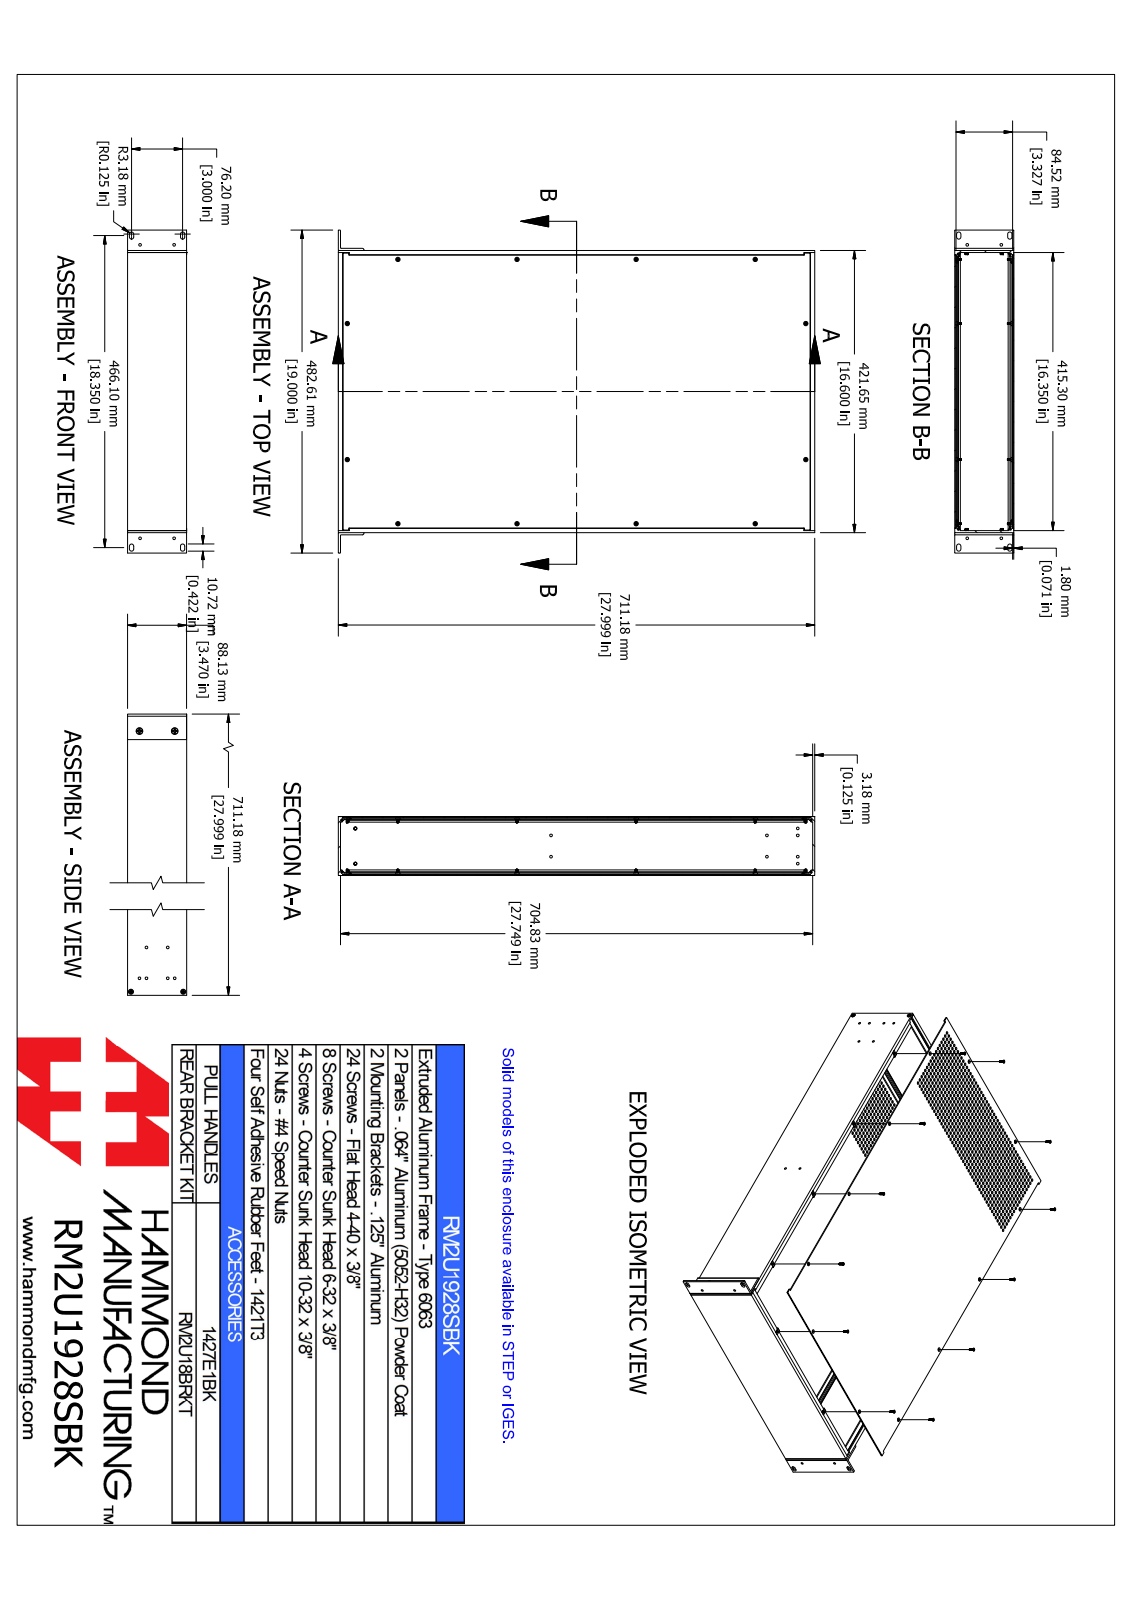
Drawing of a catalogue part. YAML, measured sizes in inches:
part_name: "RM2U1928SBK"
step_written_by: "SolidWorks 2021 (AUTOMOTIVE_DESIGN)"
units: inches
bodies: {solids: 68, faces: 2636, planar: 1076, cylindrical: 628, other: 932}
overall_size: [28.064, 19, 3.471]
volume: 114.6
surface_area: 2686
round_holes:
  - {diameter: 0.157, count: 16}
  - {diameter: 0.16, count: 12}
  - {diameter: 0.165, count: 8}
  - {diameter: 0.159, count: 6}
  - {diameter: 0.156, count: 4}
  - {diameter: 0.157, count: 4}
  - {diameter: 0.169, count: 4}
  - {diameter: 0.197, count: 2}
round_bosses_or_shafts:
  - {diameter: 0.2, count: 12}
  - {diameter: 0.112, count: 12}
  - {diameter: 0.238, count: 5}
  - {diameter: 0.138, count: 5}
  - {diameter: 0.36, count: 2}
  - {diameter: 0.19, count: 2}
partial_cylinders:
  - {radius: 0.01, count: 96}
  - {radius: 0.024, count: 96}
  - {radius: 0.009, count: 48}
  - {radius: 0.014, count: 48}
  - {radius: 0.015, count: 16}
  - {radius: 0.038, count: 16}
  - {radius: 0.039, count: 16}
  - {radius: 0.035, count: 10}
face_to_face_distances: [0.071, 3.399, 3.47, 3.398, 0.071, 3.328, 0.125, 16.476, 16.601, 16.35]
hole_center_spacings: [7, 17.049, 14, 20.92, 26.707, 4.803, 8, 10.662]
